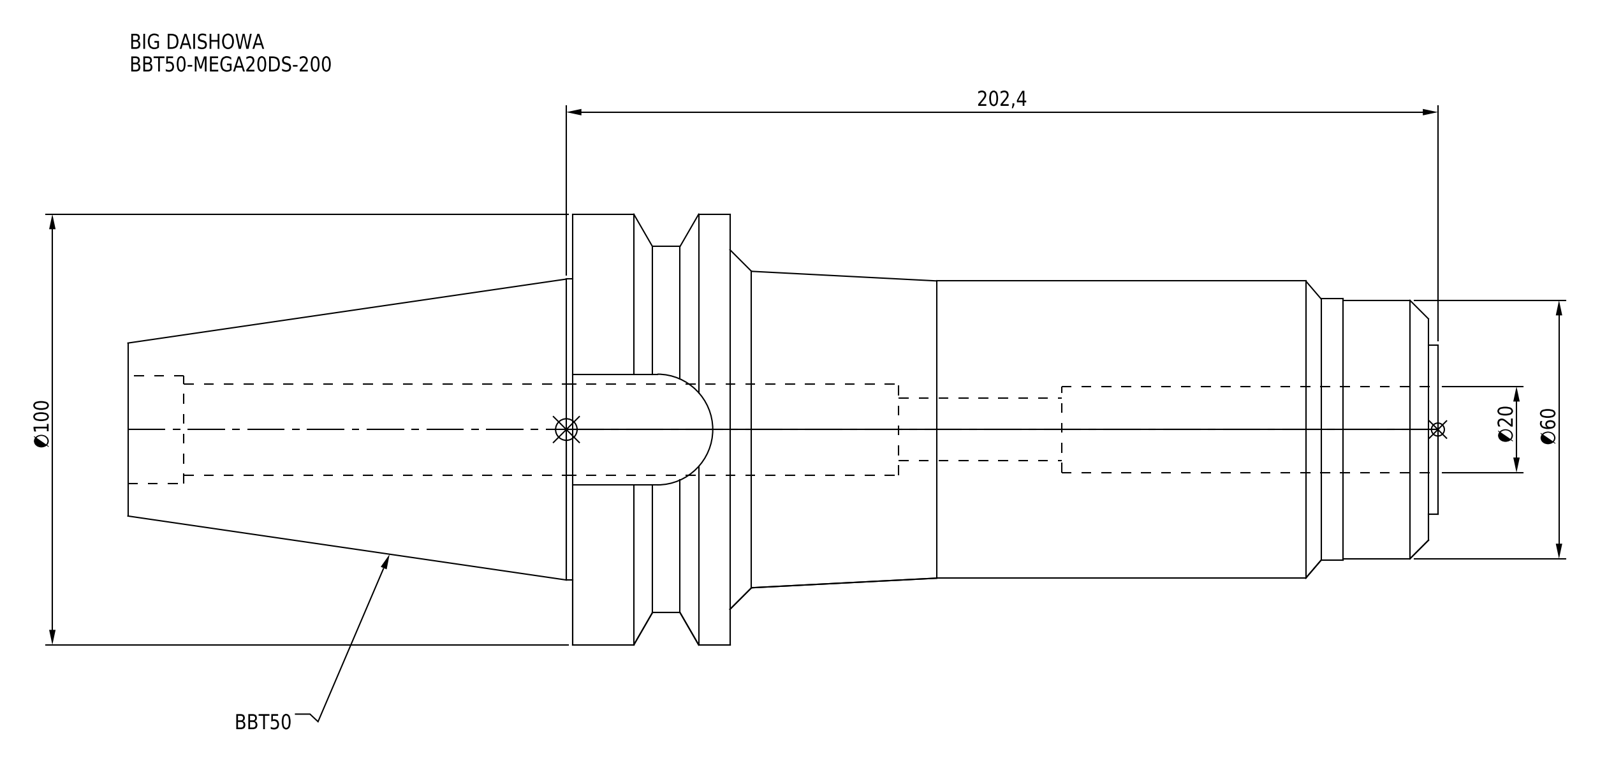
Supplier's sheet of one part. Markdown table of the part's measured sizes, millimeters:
| quantity | value |
| --- | --- |
| part name | BBT50-MEGA20DS-200 |
| STEP written by | CREO PARAMETRIC BY PTC INC, 2016380 (AUTOMOTIVE_DESIGN) |
| units | millimeters |
| bodies | 1 solid, 57 faces (15 planar, 28 cylindrical, 14 other) |
| overall size | 304.2 × 100 × 100 |
| volume | 999 991 mm³ |
| surface area | 97 293 mm² |
| round holes (diameter × count) | 14.5 × 1, 20 × 1, 21.2 × 1, 25 × 1 |
| round bosses / shafts (diameter × count) | 100 × 1, 85 × 1, 69.85 × 1, 69 × 1, 60.7 × 1, 60 × 1, 39.3 × 1 |
| partial cylindrical surfaces (radius × count) | 12.85 × 1 |
| main face-to-face distances | 36.5, 164.4, 200.9, 2.2, 162.2, 198.7, 304.2, 302, 139.8, 103.3 |
